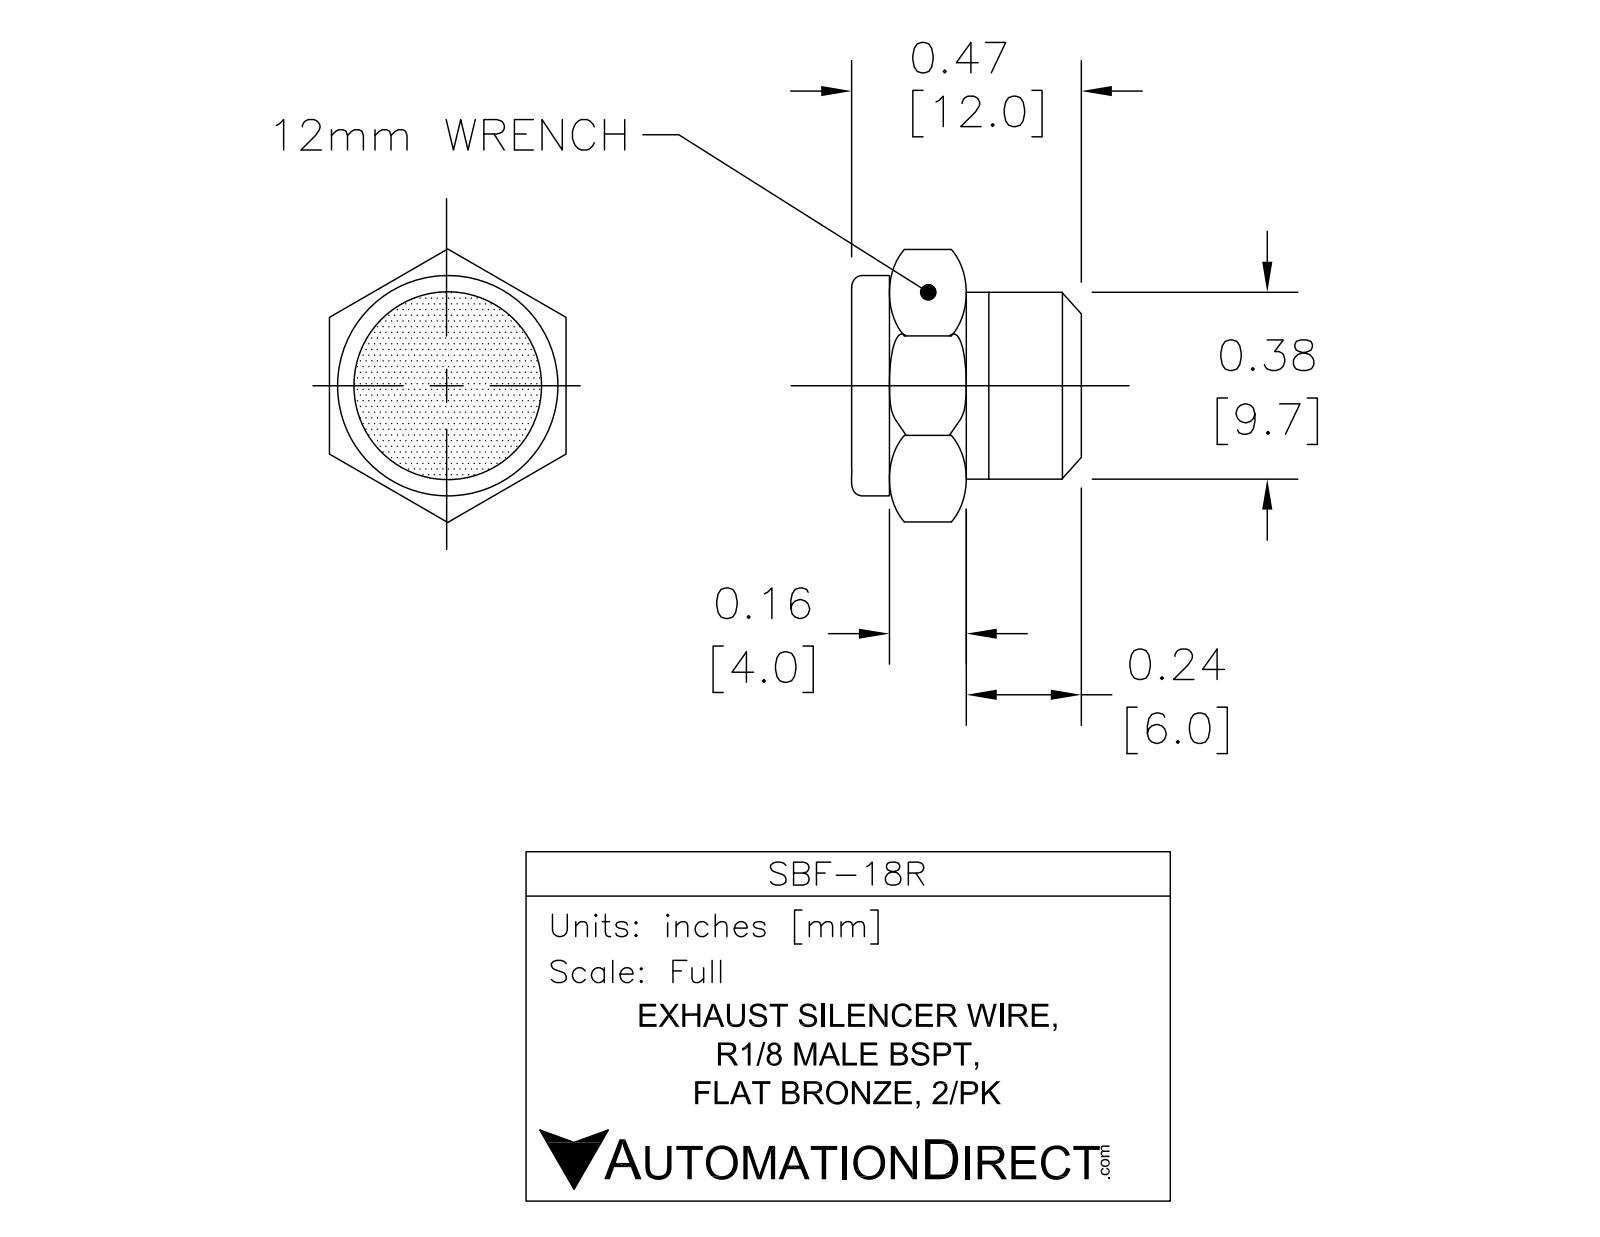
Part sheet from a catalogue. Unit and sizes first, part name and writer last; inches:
Units: inches
Overall size (bounding box): 0.47 × 0.45 × 0.39
Round holes (diameter × count): ⌀0.22 ×1
Round bosses / shafts (diameter × count): ⌀0.38 ×1, ⌀0.36 ×1
Main face-to-face distances: 0.39, 0.07, 0.4, 0.47, 0.21, 0.19, 0.26, 0.24, 0.03, 0.16
Volume: 0.037 in³ · Surface area: 1.241 in²
Bodies: 1 solid, 47 faces (12 planar, 15 cylindrical, 20 other)
Part name (STEP PRODUCT): SBF-18R
STEP written by: SolidWorks 2015 (CONFIG_CONTROL_DESIGN)
